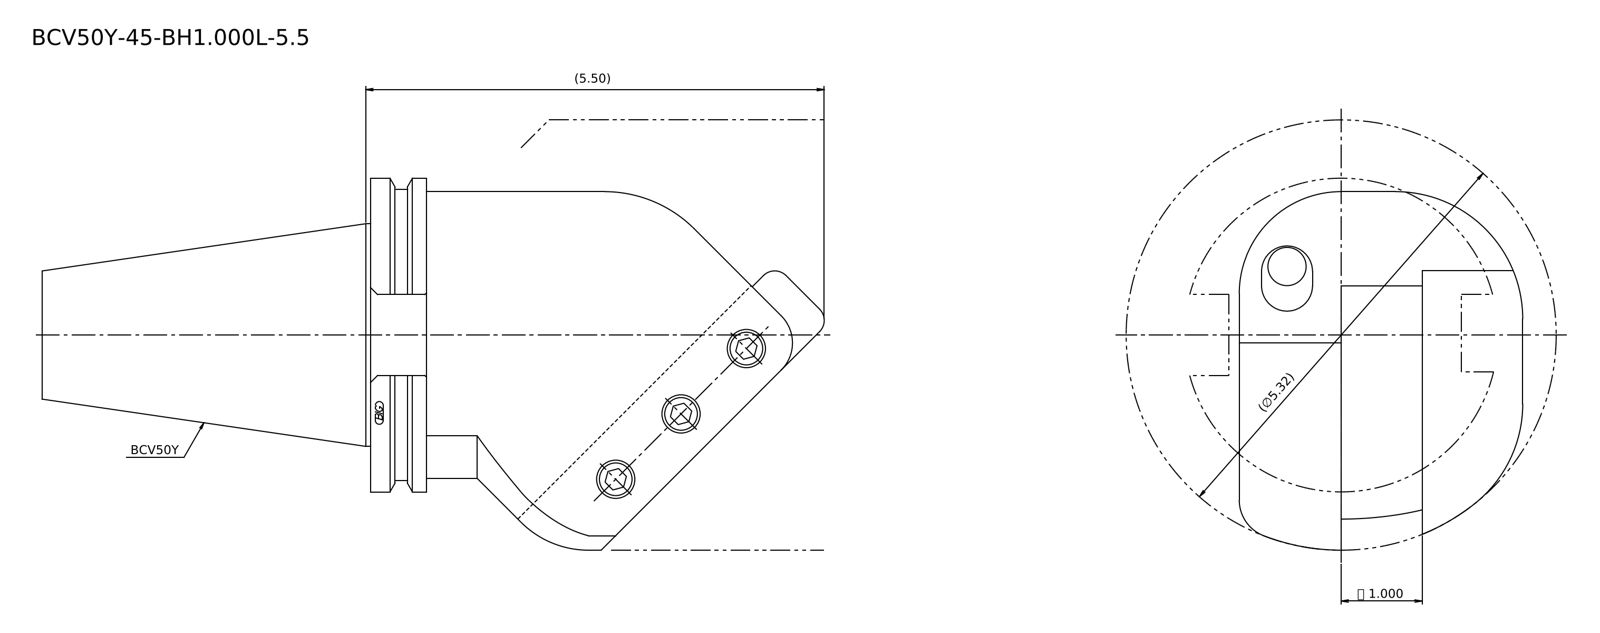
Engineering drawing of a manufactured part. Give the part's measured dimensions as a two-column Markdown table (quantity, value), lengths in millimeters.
| quantity | value |
| --- | --- |
| STEP written by | Kubotek KeyCreator 2011 V10.0.2 (22737) (automotive_design) |
| units | millimeters |
| bodies | 1 solid, 32 faces (17 planar, 11 cylindrical, 4 other) |
| overall size | 247.6 × 116.71 × 106.21 |
| volume | 1 070 000 mm³ |
| surface area | 77 032 mm² |
| round bosses / shafts (diameter × count) | 98.42 × 1, 91.29 × 1, 69.85 × 1 |
| partial cylindrical surfaces (radius × count) | 40 × 2, 12 × 1, 32 × 1, 45 × 1, 67.5 × 1 |
| main face-to-face distances | 25.4, 57.4, 32, 89, 57, 31.6, 17.55, 120.65, 103.1, 9.99 |
